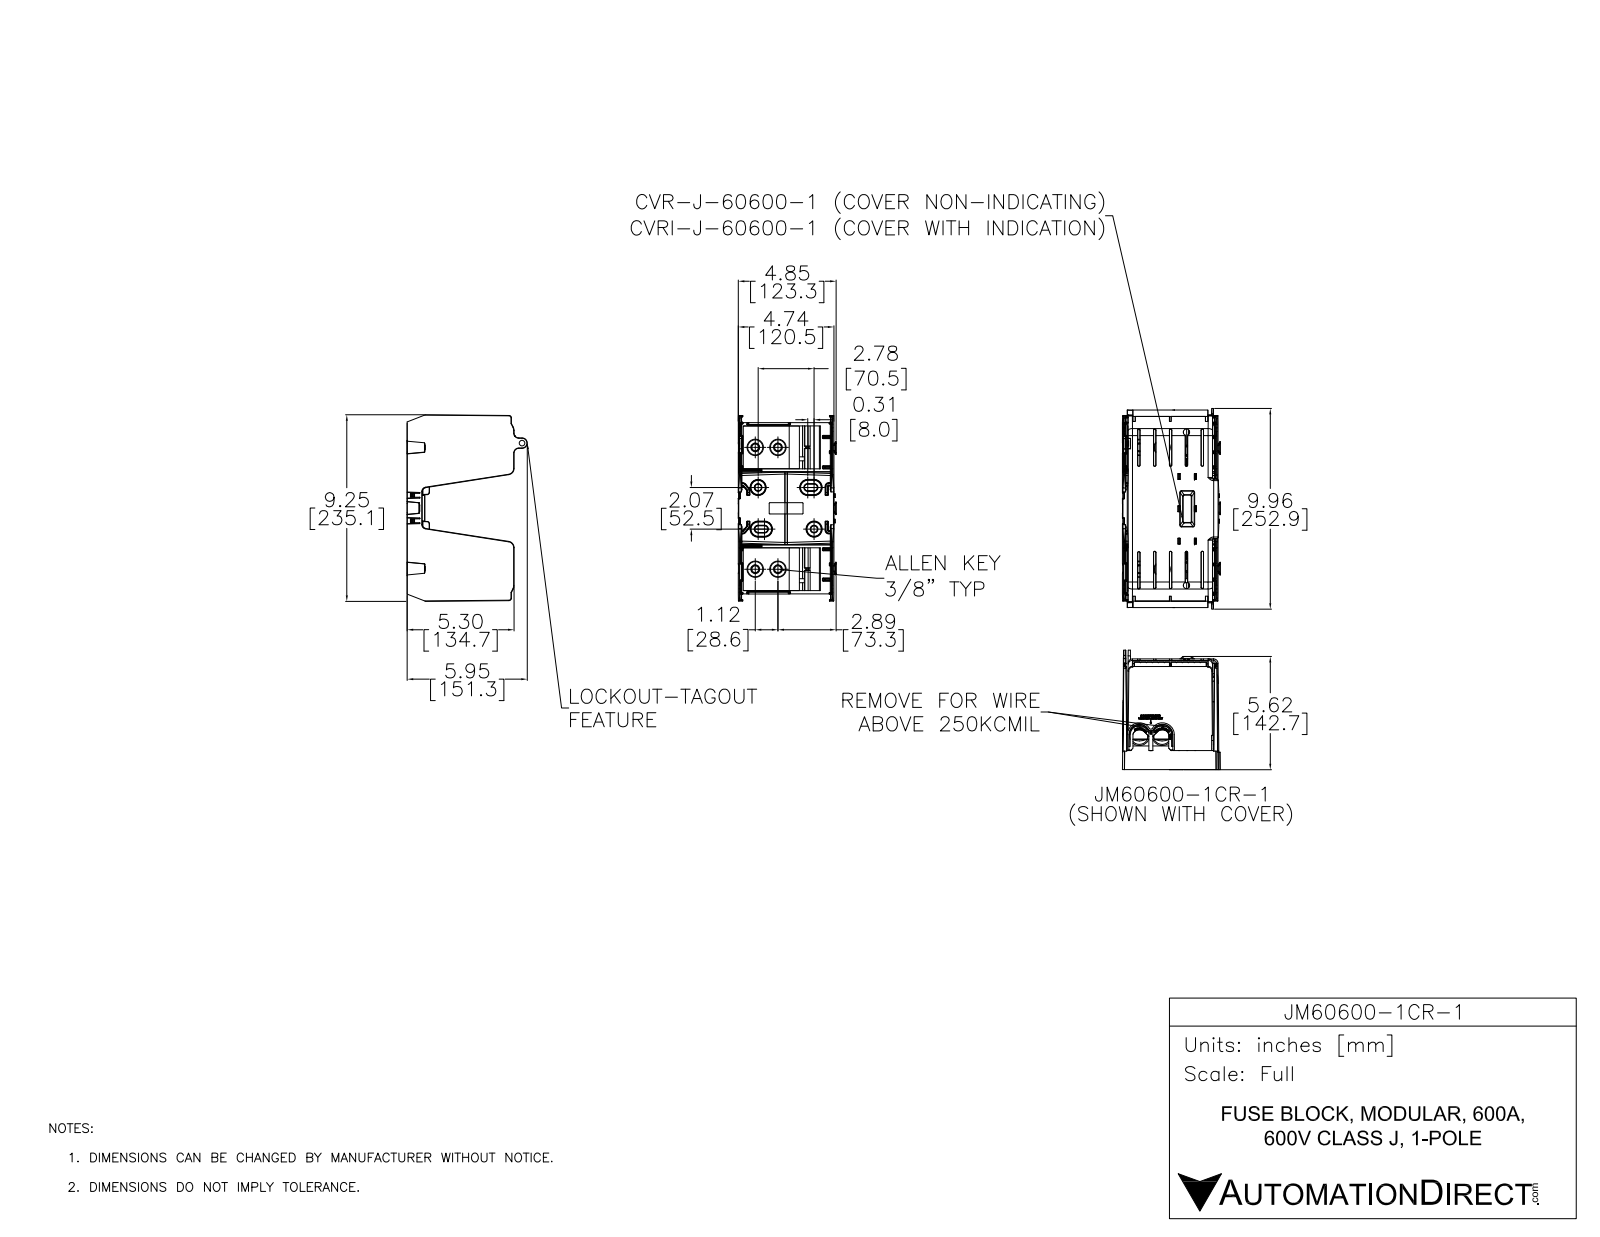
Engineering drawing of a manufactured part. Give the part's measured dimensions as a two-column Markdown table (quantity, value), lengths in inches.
| quantity | value |
| --- | --- |
| part name | JM60600-1CR-1 |
| STEP written by | SolidWorks 2021 (CONFIG_CONTROL_DESIGN) |
| units | inches |
| bodies | 0 solids, 1021 faces (328 planar, 448 cylindrical, 245 other) |
| overall size | 9.254 × 5.958 × 4.878 |
| round bosses / shafts (diameter × count) | 0.812 × 3, 0.5 × 2, 0.196 × 2, 0.875 × 1, 0.875 × 1, 0.812 × 1, 0.277 × 1 |
| partial cylindrical surfaces (radius × count) | 0.02 × 134, 0.01 × 51, 0.02 × 32, 0.014 × 21, 0.014 × 18, 0.01 × 16, 0.039 × 9, 0.015 × 6 |
| main face-to-face distances | 0.125, 0.048, 4.602, 0.95, 4.601, 0.998, 1.123, 0.173, 0.5, 4.548 |
